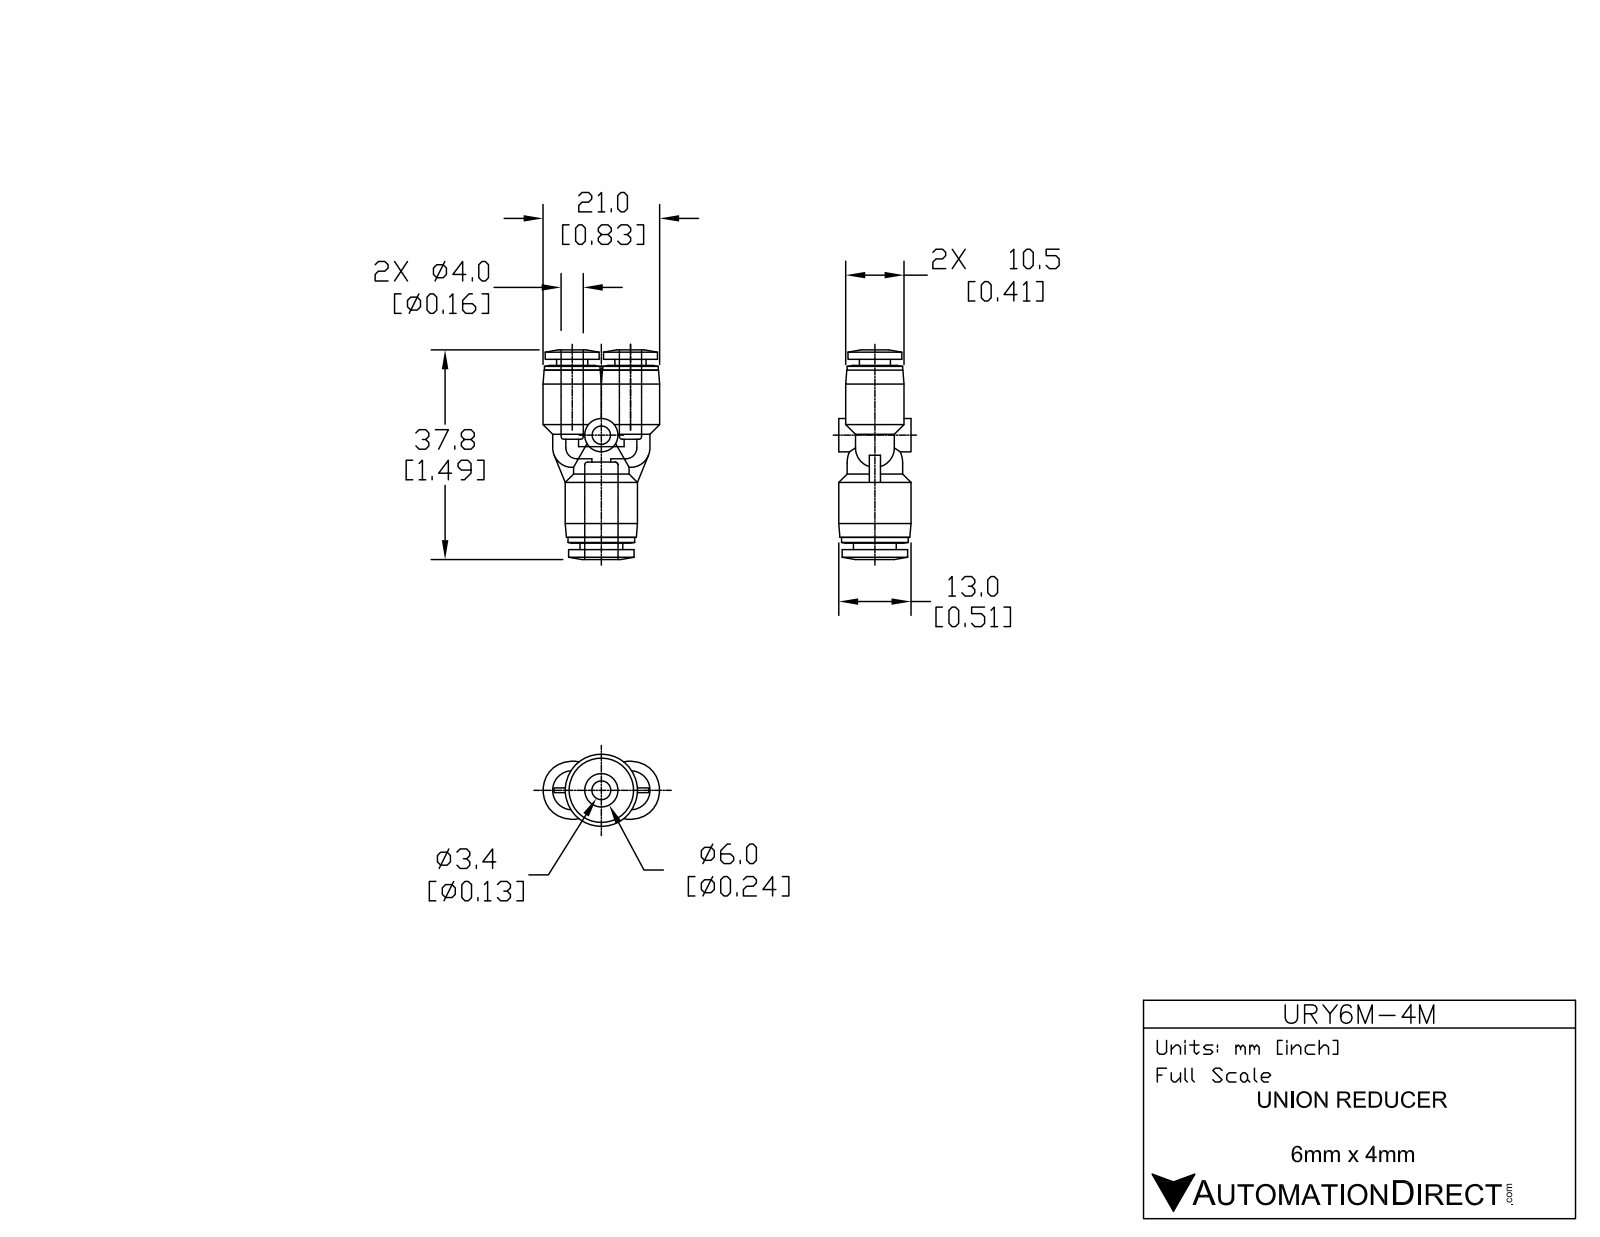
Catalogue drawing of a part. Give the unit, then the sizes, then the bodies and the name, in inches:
Units: inches
Overall size (bounding box): 1.478 × 0.827 × 0.512
Round holes (diameter × count): ⌀0.169 ×2, ⌀0.13 ×1, ⌀0.248 ×1
Round bosses / shafts (diameter × count): ⌀0.394 ×3, ⌀0.413 ×2, ⌀0.382 ×2, ⌀0.22 ×2, ⌀0.512 ×1, ⌀0.472 ×1, ⌀0.465 ×1, ⌀0.303 ×1
Partial cylindrical surfaces — rounded edges, fillets, slot ends (radius × count): R0.138 ×2
Main face-to-face distances: 1.341, 1.297, 0.043, 0.045, 1.252, 1.295, 0.217, 0.295, 0.622, 0.577
Hole centre spacings: 0.207, 0.413
Volume: 0.236 in³ · Surface area: 5.456 in²
Bodies: 1 solid, 108 faces (21 planar, 44 cylindrical, 43 other)
Part name (STEP PRODUCT): URY6M-4M
STEP written by: SolidWorks 2015 (AUTOMOTIVE_DESIGN)
